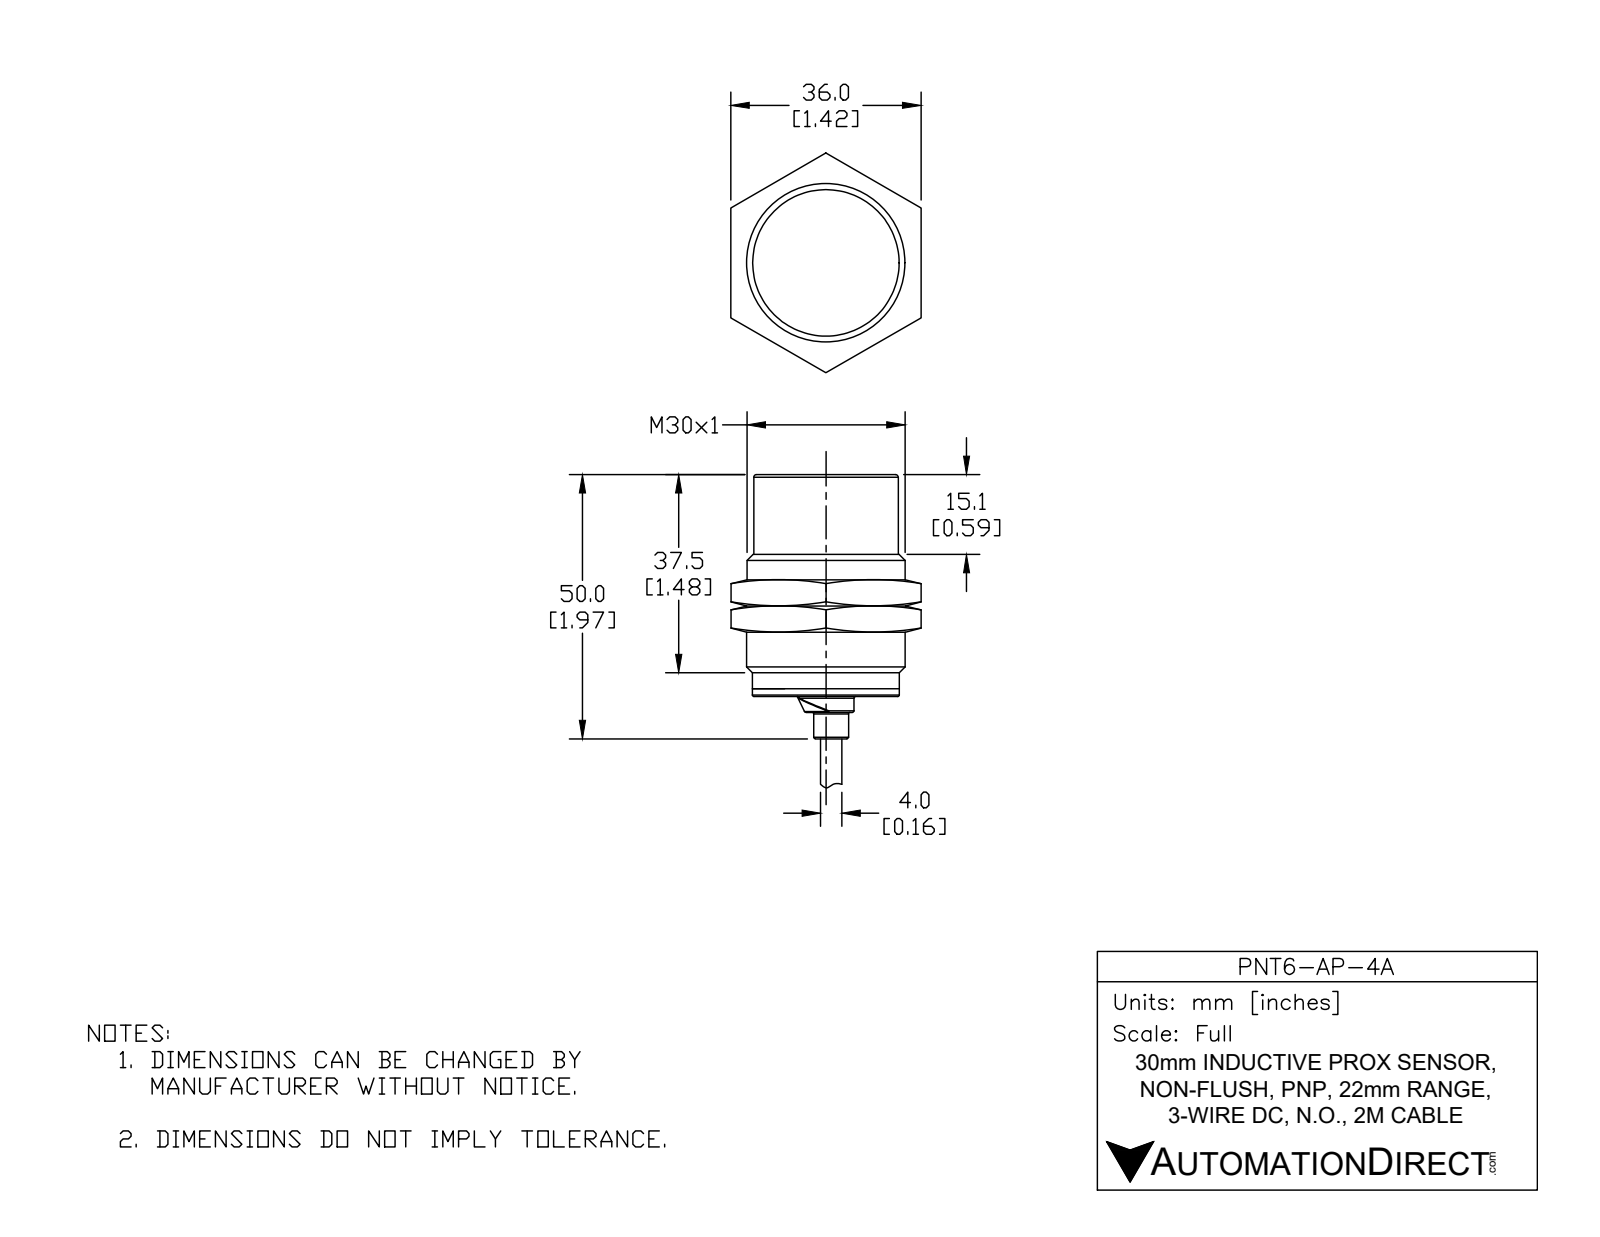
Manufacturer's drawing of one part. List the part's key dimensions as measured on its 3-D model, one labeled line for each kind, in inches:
Part name (STEP PRODUCT): PNT6-AP-4A
STEP written by: SolidWorks 2017 (AUTOMOTIVE_DESIGN)
Units: inches
Bodies: 1 solid, 77 faces (15 planar, 30 cylindrical, 32 other)
Overall size (bounding box): 3.969 × 1.181 × 1.181
Volume: 1.84 in³ · Surface area: 9.715 in²
Round holes (diameter × count): ⌀0.162 ×1
Round bosses / shafts (diameter × count): ⌀0.049 ×6, ⌀1.181 ×1, ⌀1.095 ×1, ⌀1.094 ×1, ⌀0.417 ×1, ⌀0.26 ×1, ⌀0.157 ×1
Partial cylindrical surfaces — rounded edges, fillets, slot ends (radius × count): R0.077 ×1
Main face-to-face distances: 1.654, 1.772, 0.118, 1.969, 0.315, 0.197, 3.969, 2.315, 2.197, 2
